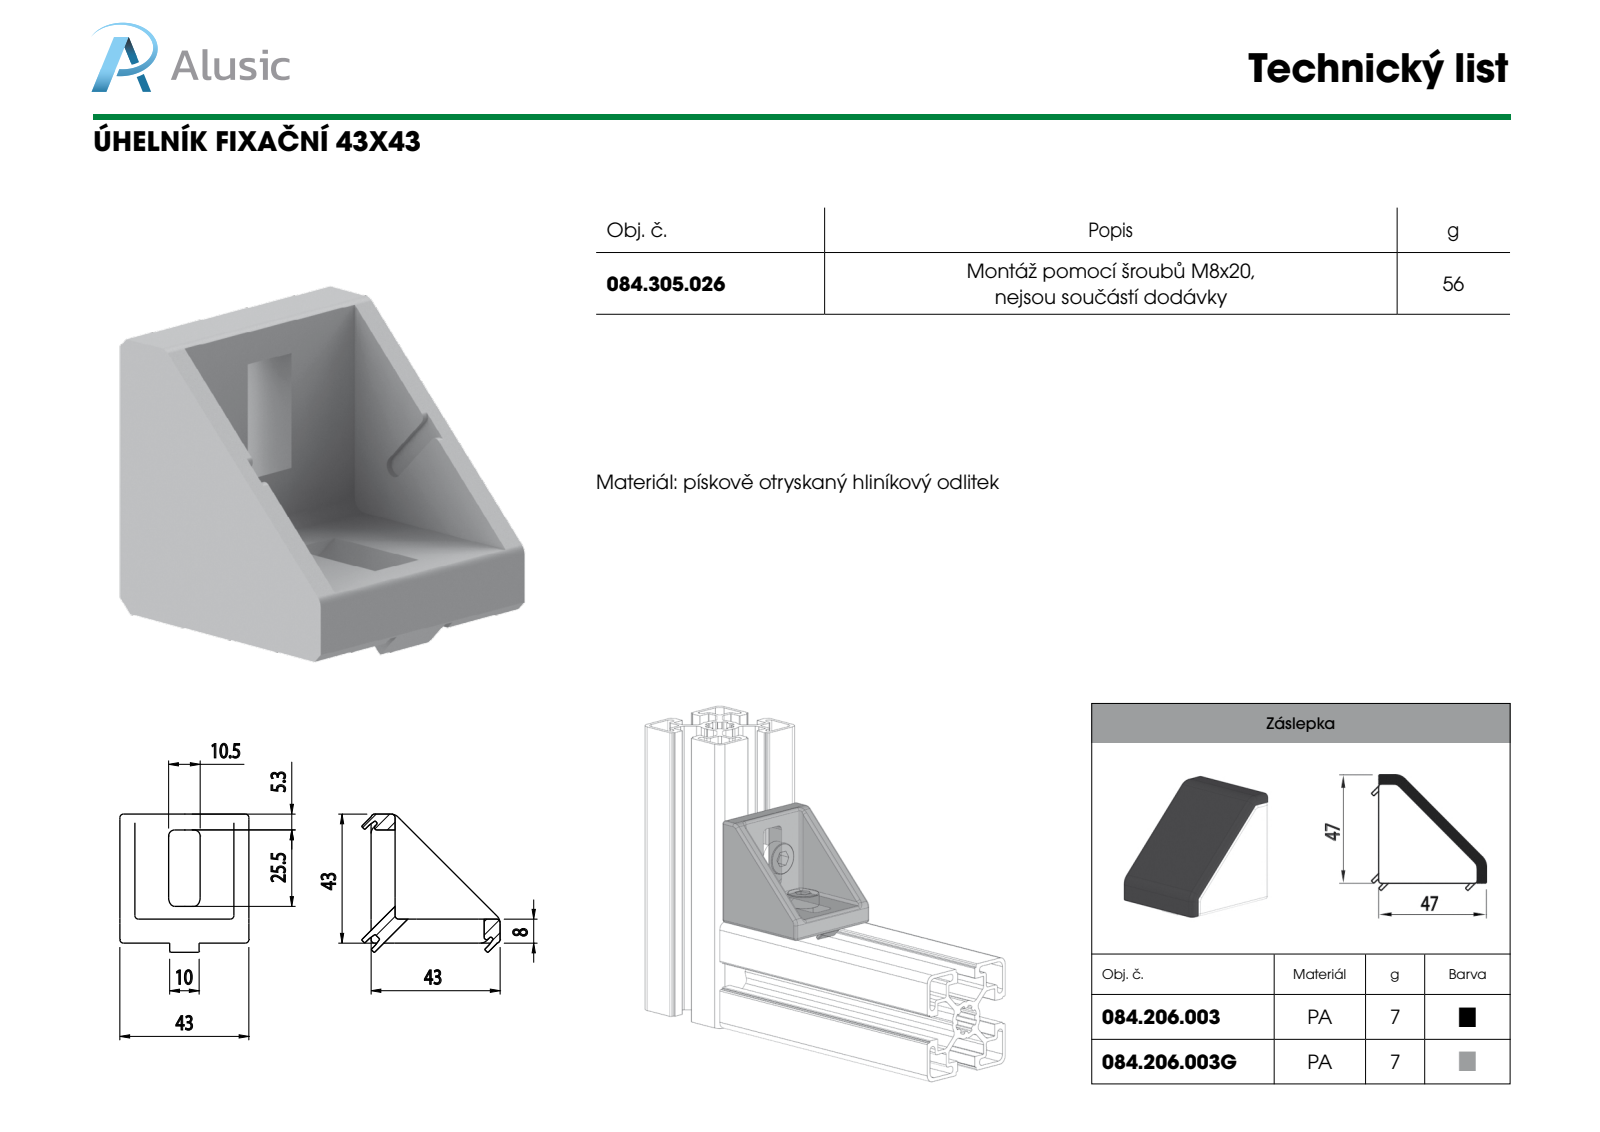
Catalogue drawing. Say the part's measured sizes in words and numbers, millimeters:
The part is named "084.305.026". Its 3-D file was written by "SolidWorks 2011 (CONFIG_CONTROL_DESIGN)". It is 1 solid with 96 faces: 85 planar, 11 cylindrical and 0 other. Overall it measures 43.77 by 43.77 by 42 millimeters. Its volume is 20 131 cubic millimeters and its surface area 13 231 square millimeters. Partial cylindrical surfaces (rounded edges, fillets, slot ends): 3 of radius 2, 2 of radius 1, 1 of radius 1.5. The main face-to-face distances are 3.5, 13, 25.5, 3, 42, 3.1, 12.5, 0.5, 6.7, 9.8.
